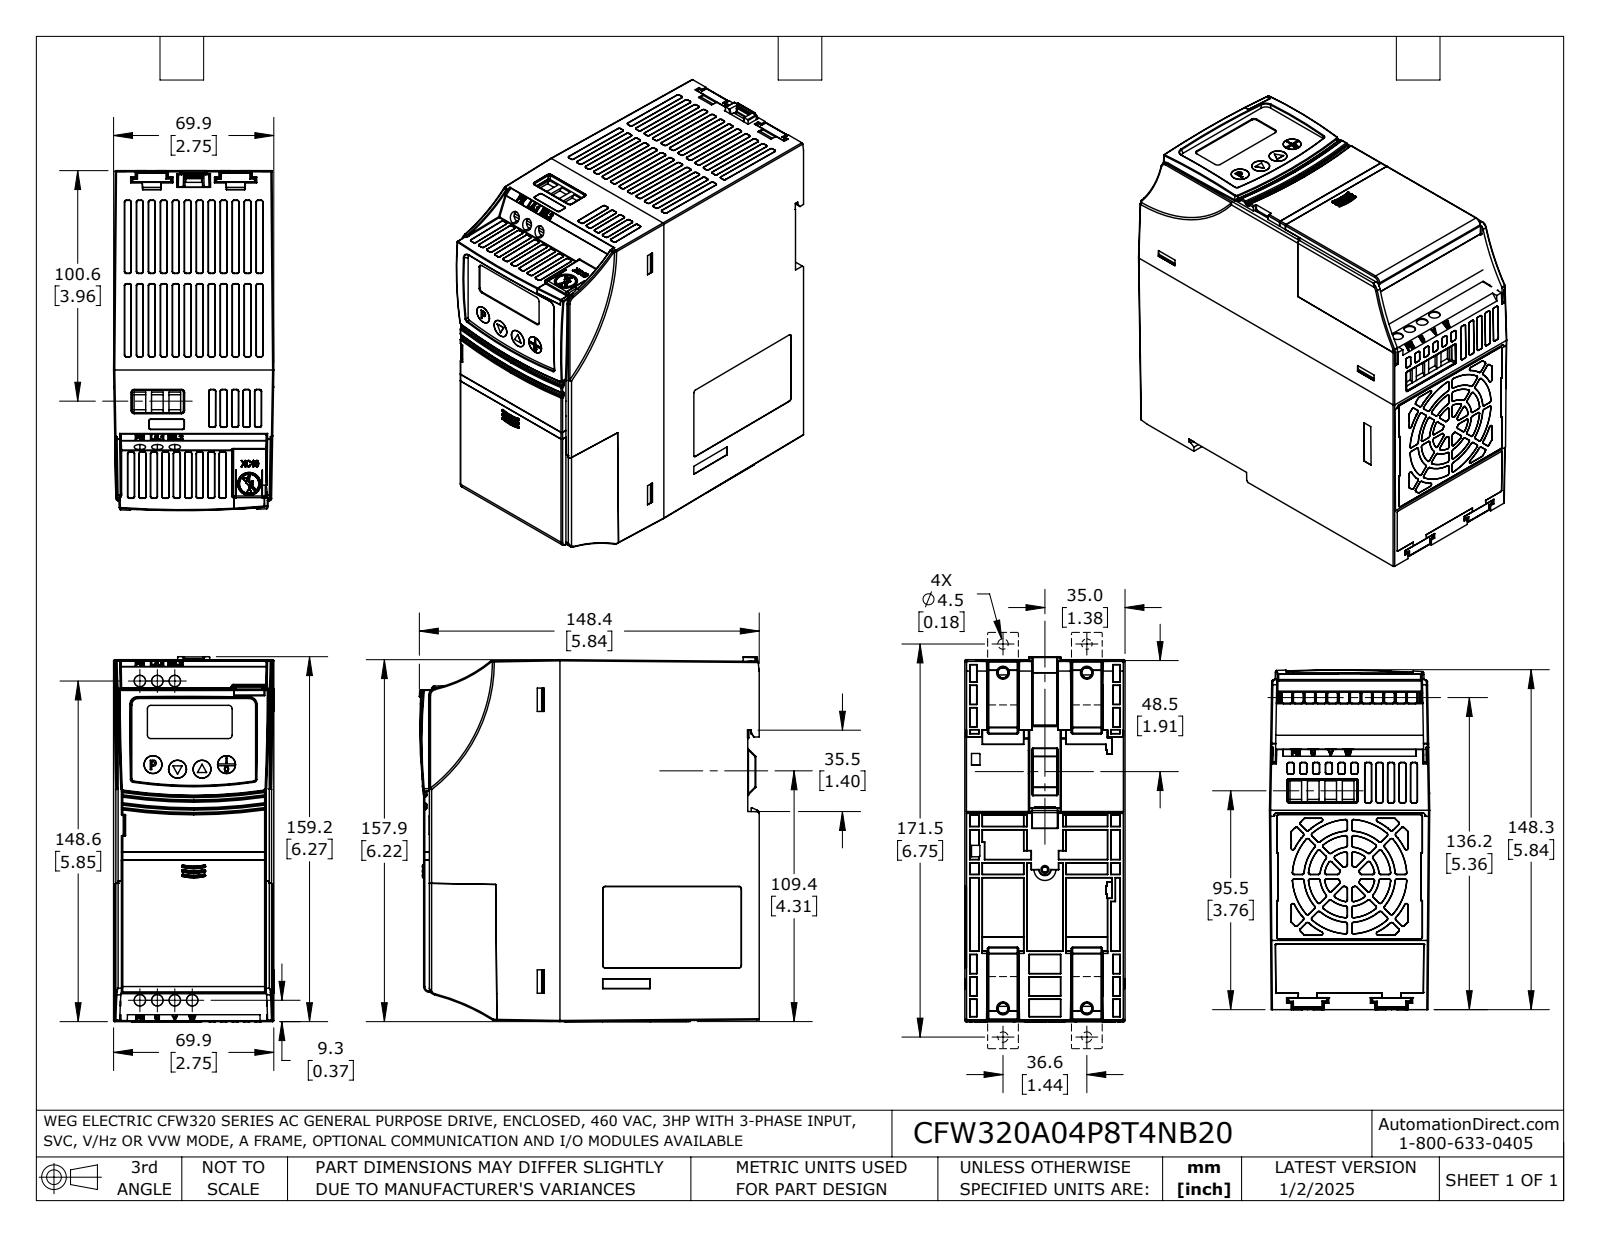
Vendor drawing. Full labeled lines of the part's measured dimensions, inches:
Part name (STEP PRODUCT): CFW320A04P8T4NB20
STEP written by: SolidWorks 2021 (AUTOMOTIVE_DESIGN)
Units: inches
Bodies: 6 solids, 3715 faces (1587 planar, 853 cylindrical, 1275 other)
Overall size (bounding box): 6.269 × 5.841 × 2.754
Volume: 15.24 in³ · Surface area: 309 in²
Round holes (diameter × count): ⌀0.197 ×3
Partial cylindrical surfaces — rounded edges, fillets, slot ends (radius × count): R0.012 ×327, R0.02 ×150, R0.039 ×13, R0.03 ×5, R0.118 ×3, R0.01 ×2, R0.098 ×1, R0.126 ×1
Main face-to-face distances: 0.07, 0.055, 0.019, 0.05, 6, 5.33, 5.275, 5.571, 5.516, 0.241
Hole centre spacings: 0.3, 0.6
